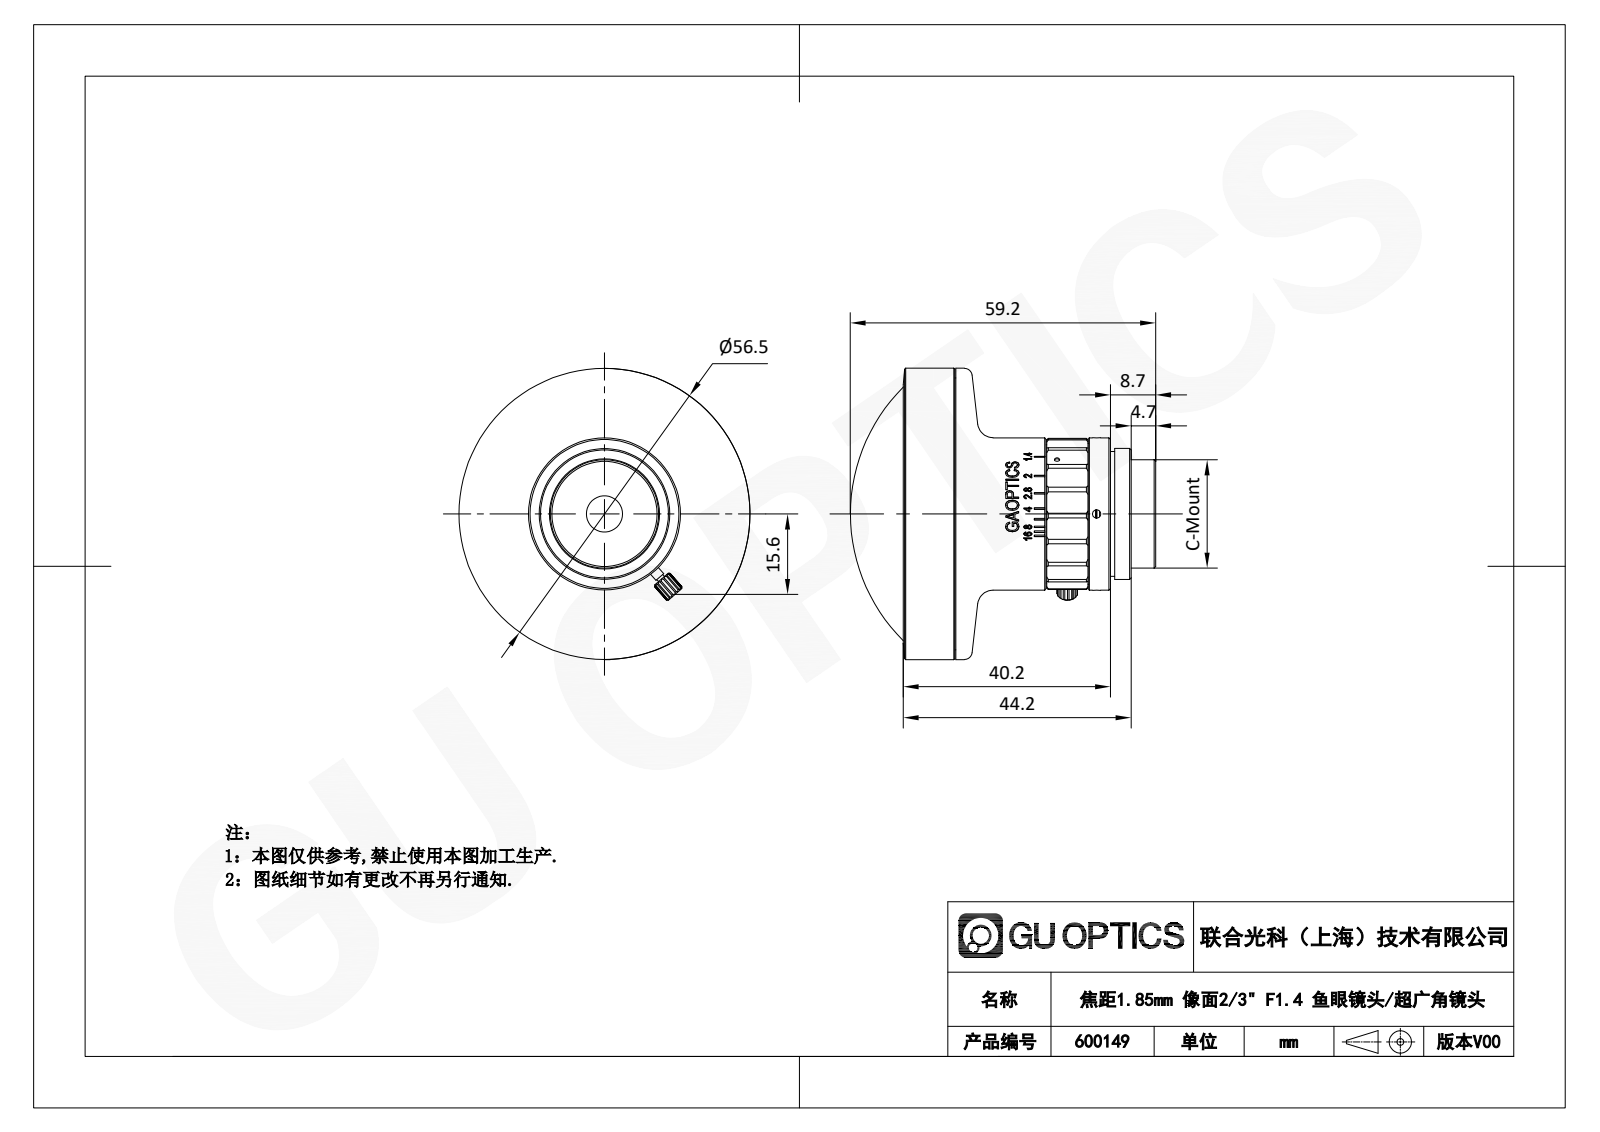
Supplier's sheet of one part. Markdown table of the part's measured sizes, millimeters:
| quantity | value |
| --- | --- |
| part name | 600149-RE1; 5000113; 600149-CM; 600149-RE3 (+8 more) |
| STEP written by | SolidWorks 2025 (AUTOMOTIVE_DESIGN) |
| units | millimeters |
| bodies | 33 solids, 1043 faces (312 planar, 391 cylindrical, 340 other) |
| overall size | 59.22 × 56.5 × 56.5 |
| volume | 51 870 mm³ |
| surface area | 29 796 mm² |
| round holes (diameter × count) | 0.8 × 12, 1.22 × 6, 1.6 × 3, 1 × 1, 7.05 × 1, 7.15 × 1, 7.25 × 1, 7.5 × 1, 7.56 × 1, 7.94 × 1, 8 × 1, 8.15 × 1 |
| round bosses / shafts (diameter × count) | 1.2 × 12, 2 × 3, 56.5 × 1, 53.5 × 1, 52.7 × 1, 29.5 × 1, 27.3 × 1, 26.8 × 1 |
| partial cylindrical surfaces (radius × count) | 1.5 × 24, 4 × 24, 0.1 × 15, 0.61 × 6, 8 × 6, 0.5 × 2, 2 × 1, 10.6 × 1 |
| main face-to-face distances | 0.7, 2.68, 1.98, 2.64, 36.18, 3, 4, 6.68, 5.98, 35.6 |
| hole center spacings | 6.5, 6.43, 5.33, 11.26, 12.87, 1.28, 7.54, 10.51 |
